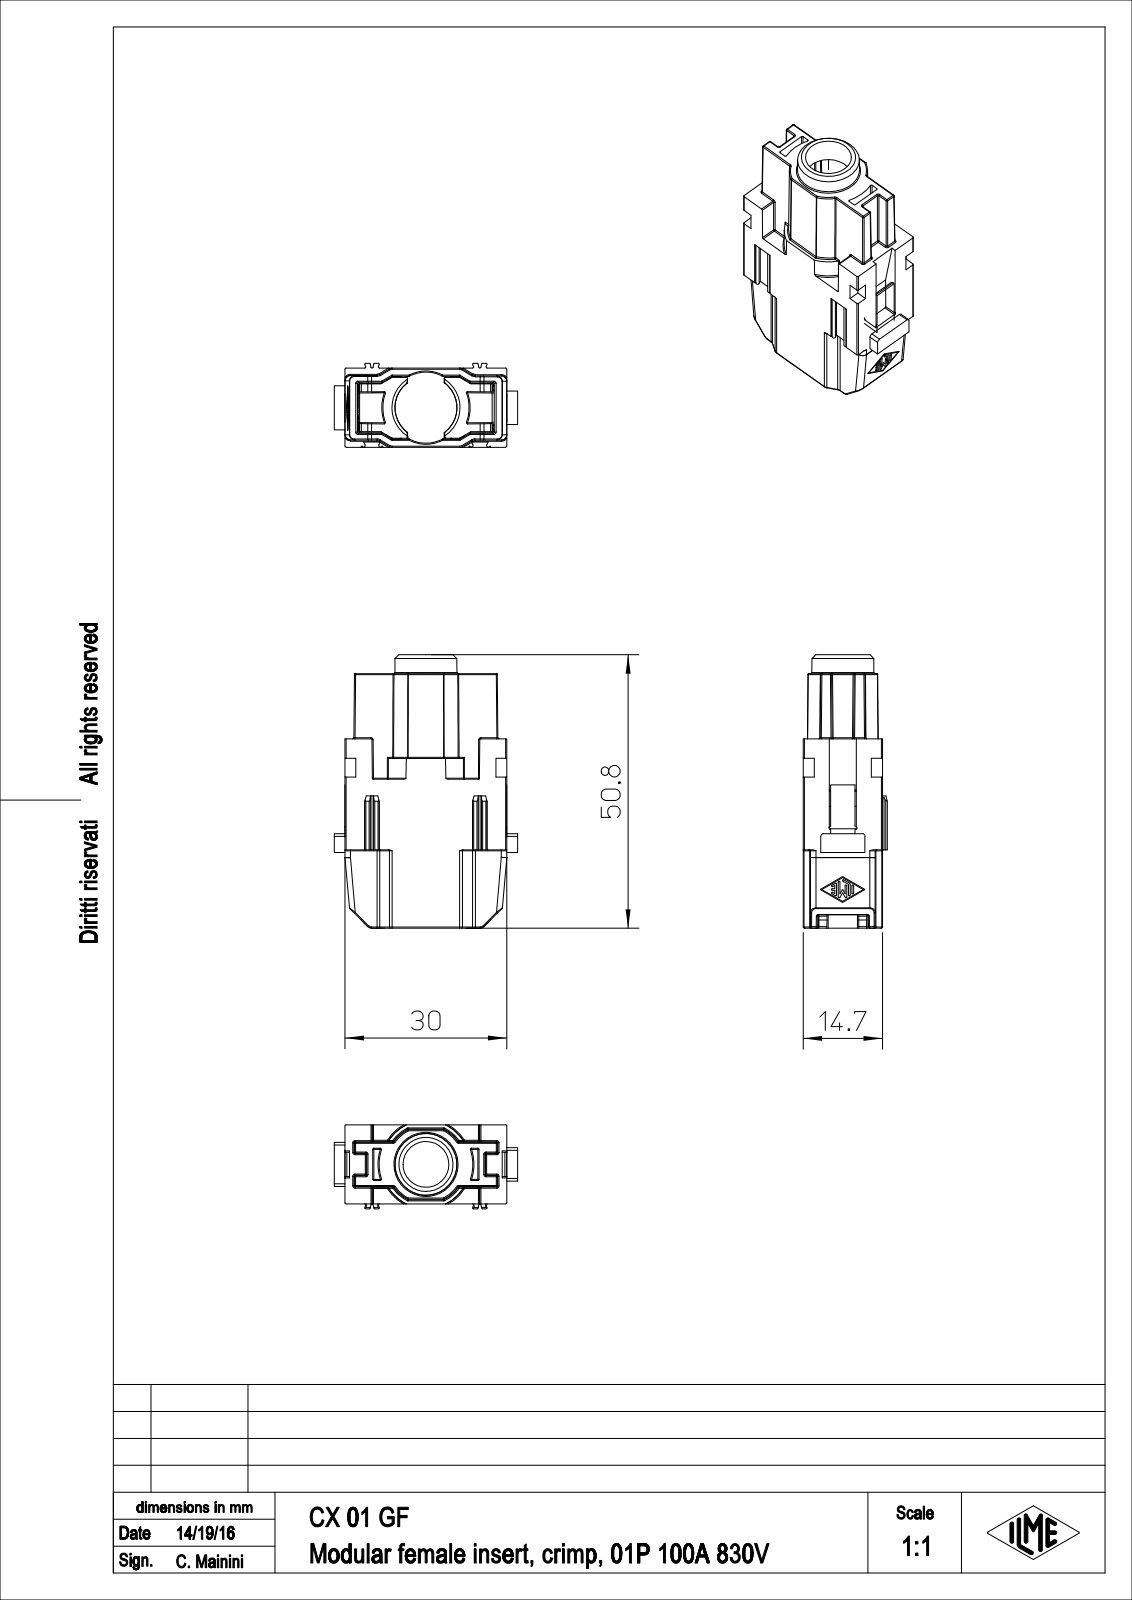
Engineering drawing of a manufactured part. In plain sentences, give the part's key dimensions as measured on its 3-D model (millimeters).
The part is named "CX_01_GF". Its 3-D file was written by "PTC Creo Elements/Direct Modeling 19.0E 27-Jun-2016 (C) Parametric Technology GmbH (AUTOMOTIVE_DESIGN)". It is 1 solid with 383 faces: 237 planar, 103 cylindrical and 43 other. Overall it measures 50.7 by 34 by 15.6 millimeters. Its volume is 10 794 cubic millimeters and its surface area 8 763 square millimeters. Round holes: 1 of diameter 8.5, 1 of diameter 11.5, 1 of diameter 13.3. Partial cylindrical surfaces (rounded edges, fillets, slot ends): 54 of radius 0.2, 6 of radius 0.5, 5 of radius 0.1, 4 of radius 1, 1 of radius 7.4, 1 of radius 7.5, 1 of radius 8.3, 1 of radius 8.75. The main face-to-face distances are 14.7, 1.65, 11.5, 3.2, 8.5, 4, 1.85, 3.5, 0.5, 2.35.
